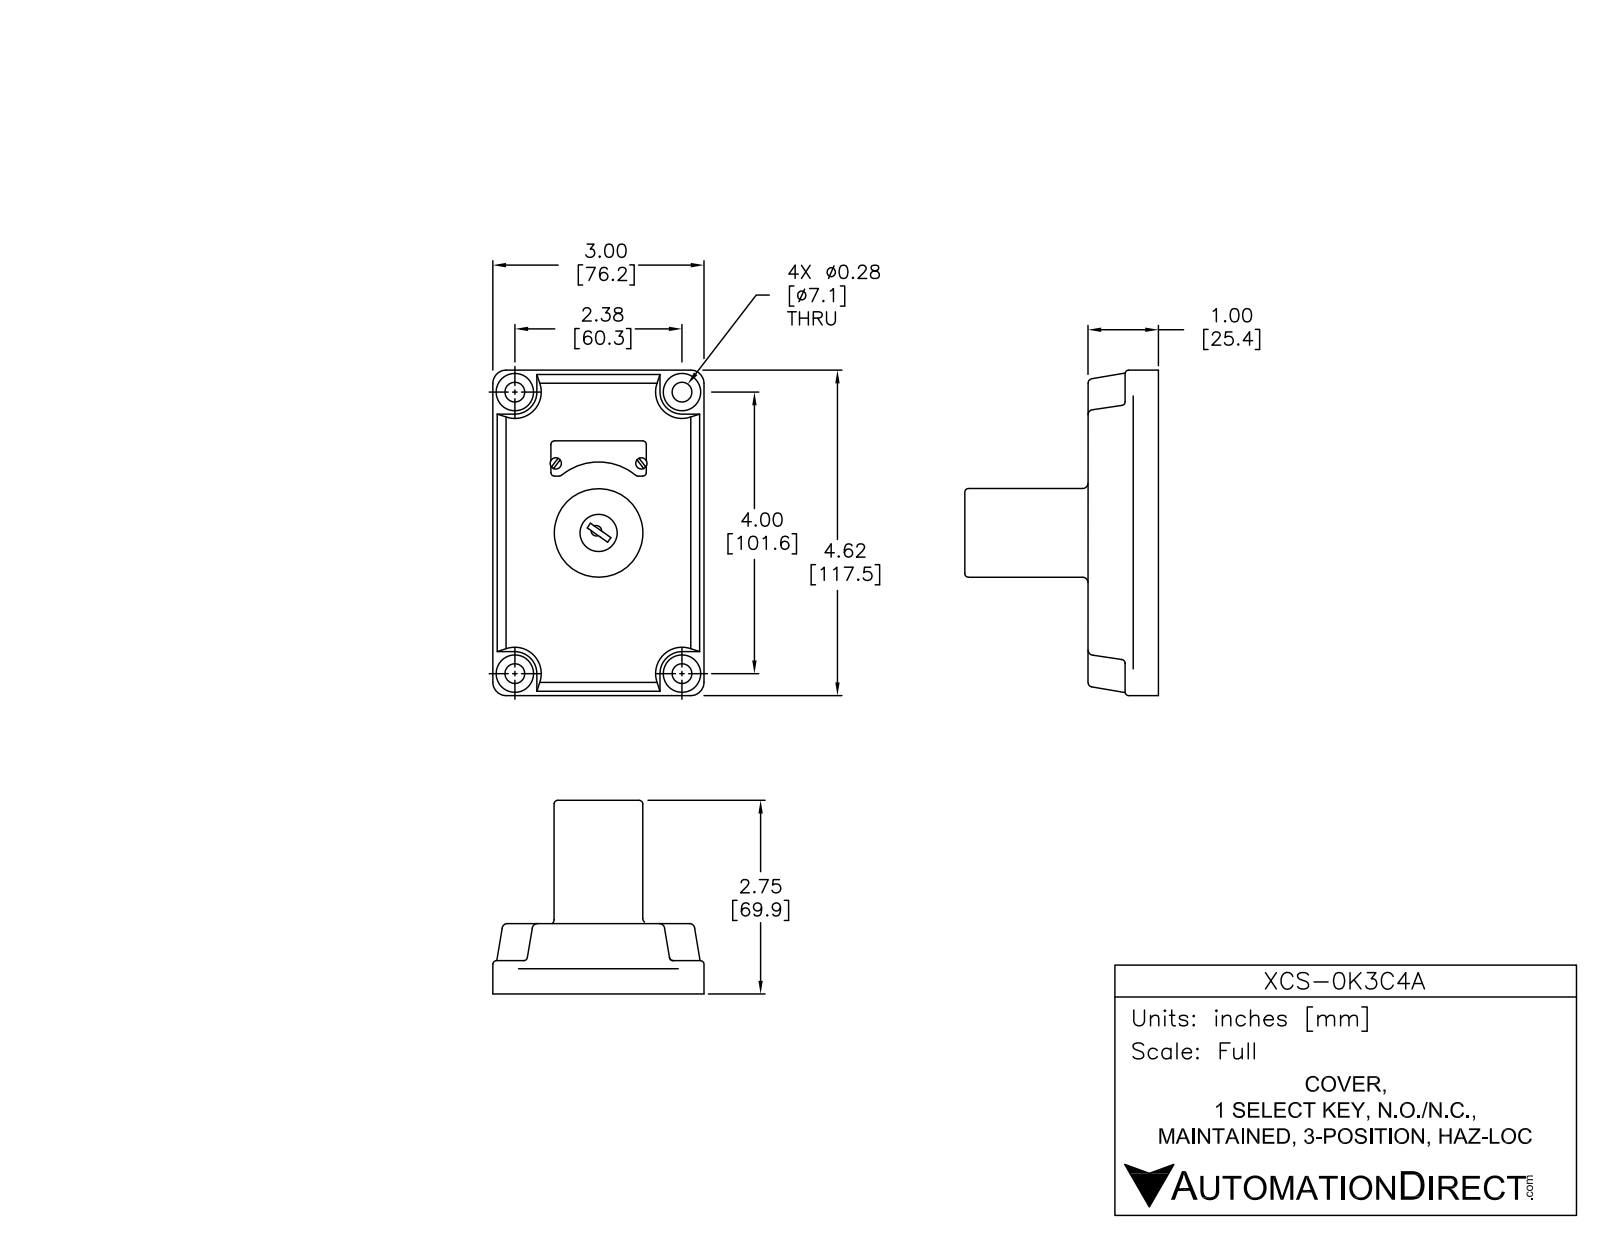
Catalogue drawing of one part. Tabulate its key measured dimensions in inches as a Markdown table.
| quantity | value |
| --- | --- |
| part name | XCS-0K3C4A |
| STEP written by | SolidWorks 2015 (AUTOMOTIVE_DESIGN) |
| units | inches |
| bodies | 14 solids, 549 faces (228 planar, 186 cylindrical, 135 other) |
| overall size | 5.487 × 4.698 × 3.1 |
| volume | 14.33 in³ |
| surface area | 99.61 in² |
| round holes (diameter × count) | 0.27 × 4, 0.196 × 2, 0.531 × 1, 0.571 × 1 |
| round bosses / shafts (diameter × count) | 0.13 × 8, 0.457 × 4, 0.25 × 4, 1.256 × 1, 0.945 × 1 |
| partial cylindrical surfaces (radius × count) | 0.01 × 28, 0.05 × 10, 0.02 × 8, 0.055 × 8, 0.079 × 8, 0.1 × 4, 0.138 × 4, 0.38 × 4 |
| main face-to-face distances | 0.525, 0.5, 1.025, 0.025, 0.035, 1.501, 2.001, 2.526, 1.466, 1.966 |
| hole center spacings | 2.327, 2.38, 4, 4.655, 0.682 |
